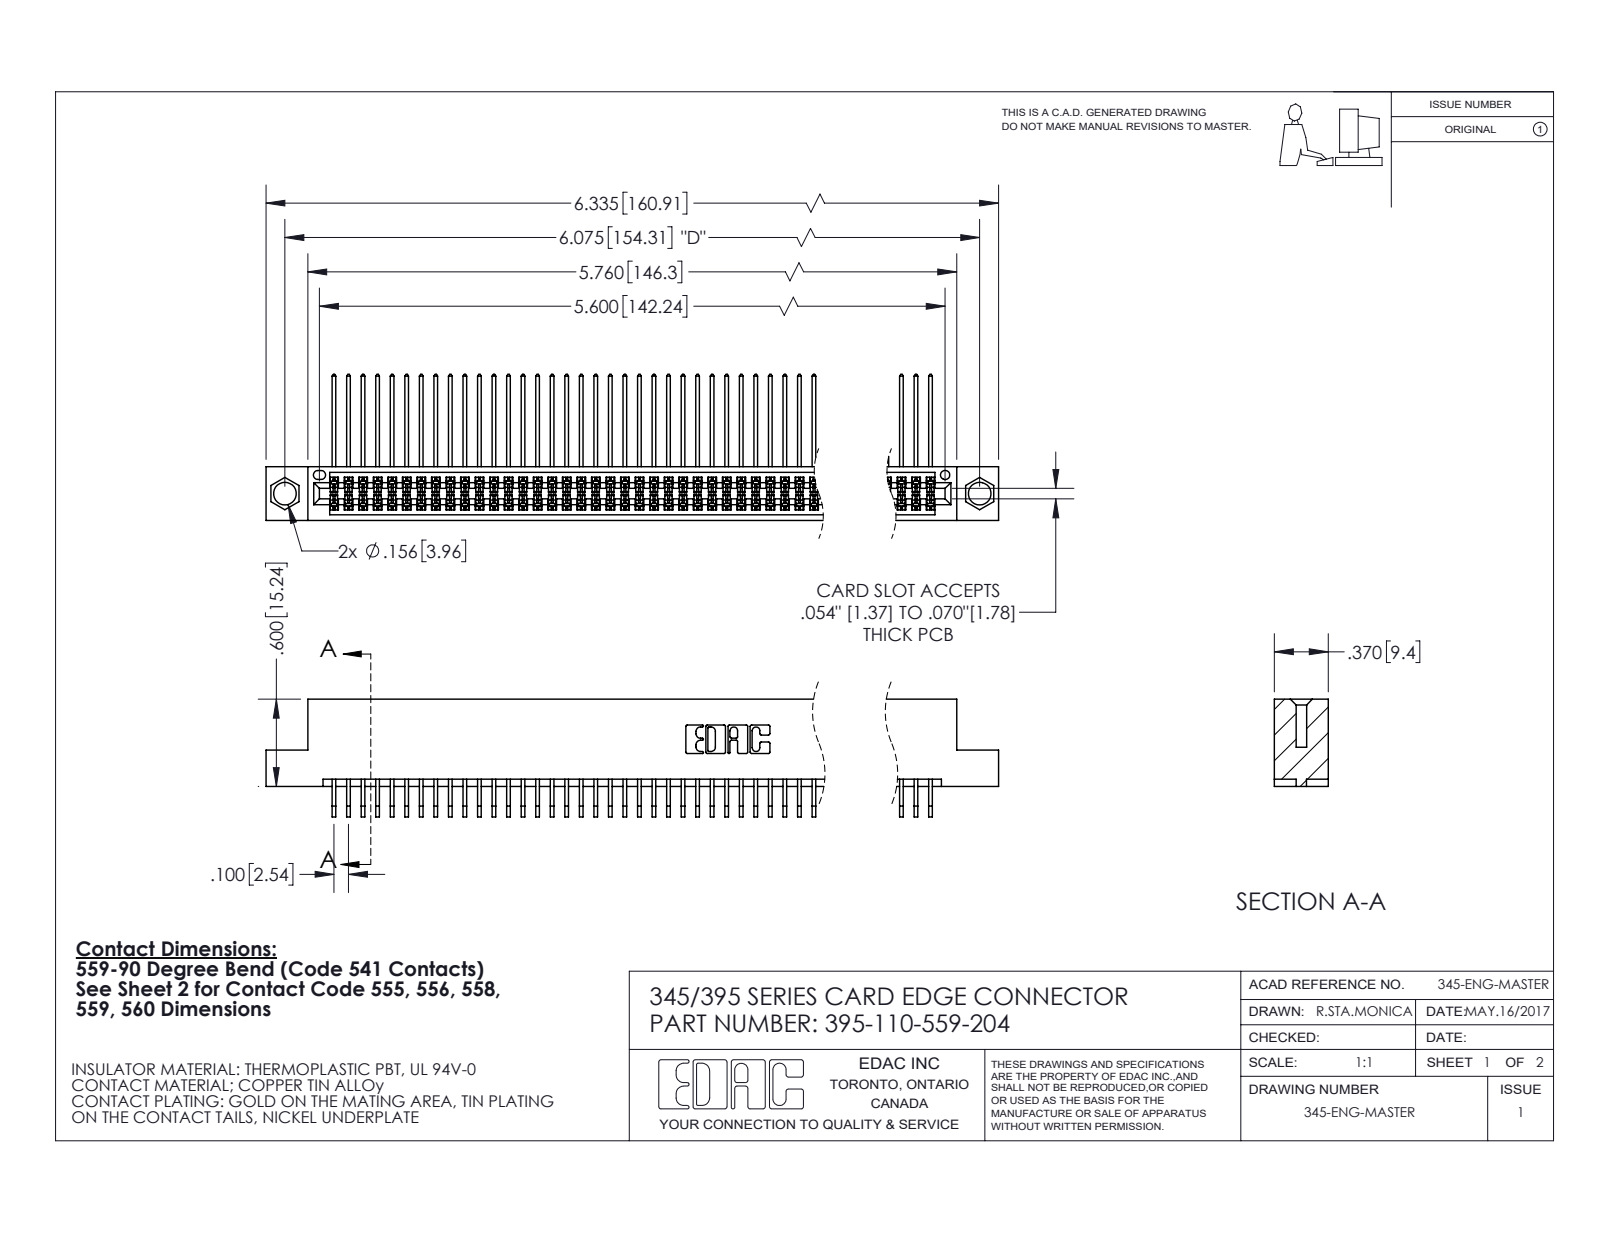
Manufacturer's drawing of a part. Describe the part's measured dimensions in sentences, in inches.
The part is named "345 Part_Flush Mounting Lugs - 0.156 Dia-TI; 395-110-559-204; 345-292-001_559 Tail - 2; 345-292-001_558 559 Tail - 1". Its 3-D file was written by "SolidWorks 2020 (CONFIG_CONTROL_DESIGN)". It is 111 solids with 5860 faces: 3944 planar, 1916 cylindrical and 0 other. Overall it measures 6.335 by 1.005 by 0.809 inches. Its volume is 0.993 cubic inches and its surface area 42.09 square inches. Round holes: 2 of diameter 0.156, 1 of diameter 0.064. Partial cylindrical surfaces (rounded edges, fillets, slot ends): 220 of radius 0.006, 22 of radius 0.01, 6 of radius 0.007, 6 of radius 0.031, 3 of radius 0.026, 2 of radius 0.014, 2 of radius 0.019, 2 of radius 0.022. The main face-to-face distances are 0.072, 0.298, 0.2, 0.37, 0.098, 0.272, 0.025, 0.225, 0.175, 0.15. The hole center spacings are 0.27, 5.839, 6.075.
